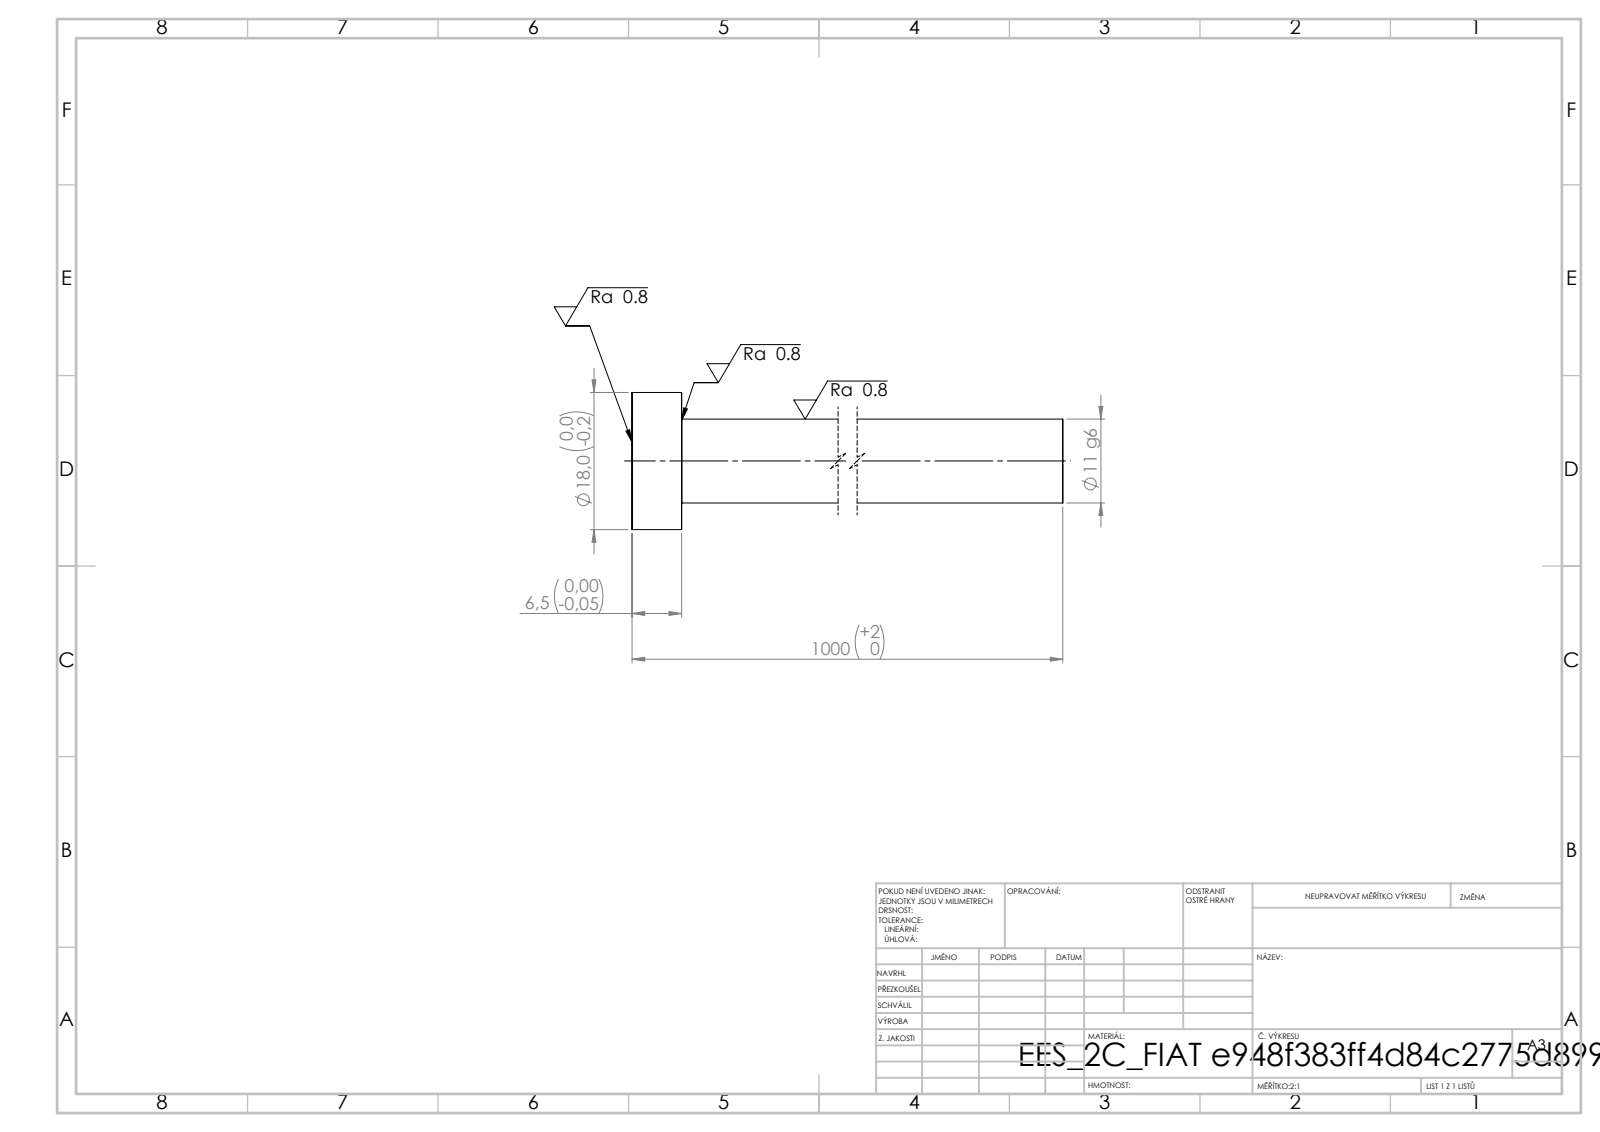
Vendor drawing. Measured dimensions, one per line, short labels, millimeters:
written by: SolidWorks 2019 (CONFIG_CONTROL_DESIGN)
unit: mm
bodies: 1 solid, 7 faces (3 planar, 4 cylindrical, 0 other)
size: 1000 × 18 × 18
volume: 96 070 mm³; area: 35 209 mm²
bosses: 1× ⌀18, 1× ⌀11
face distances: 6.5, 1000, 993.5
